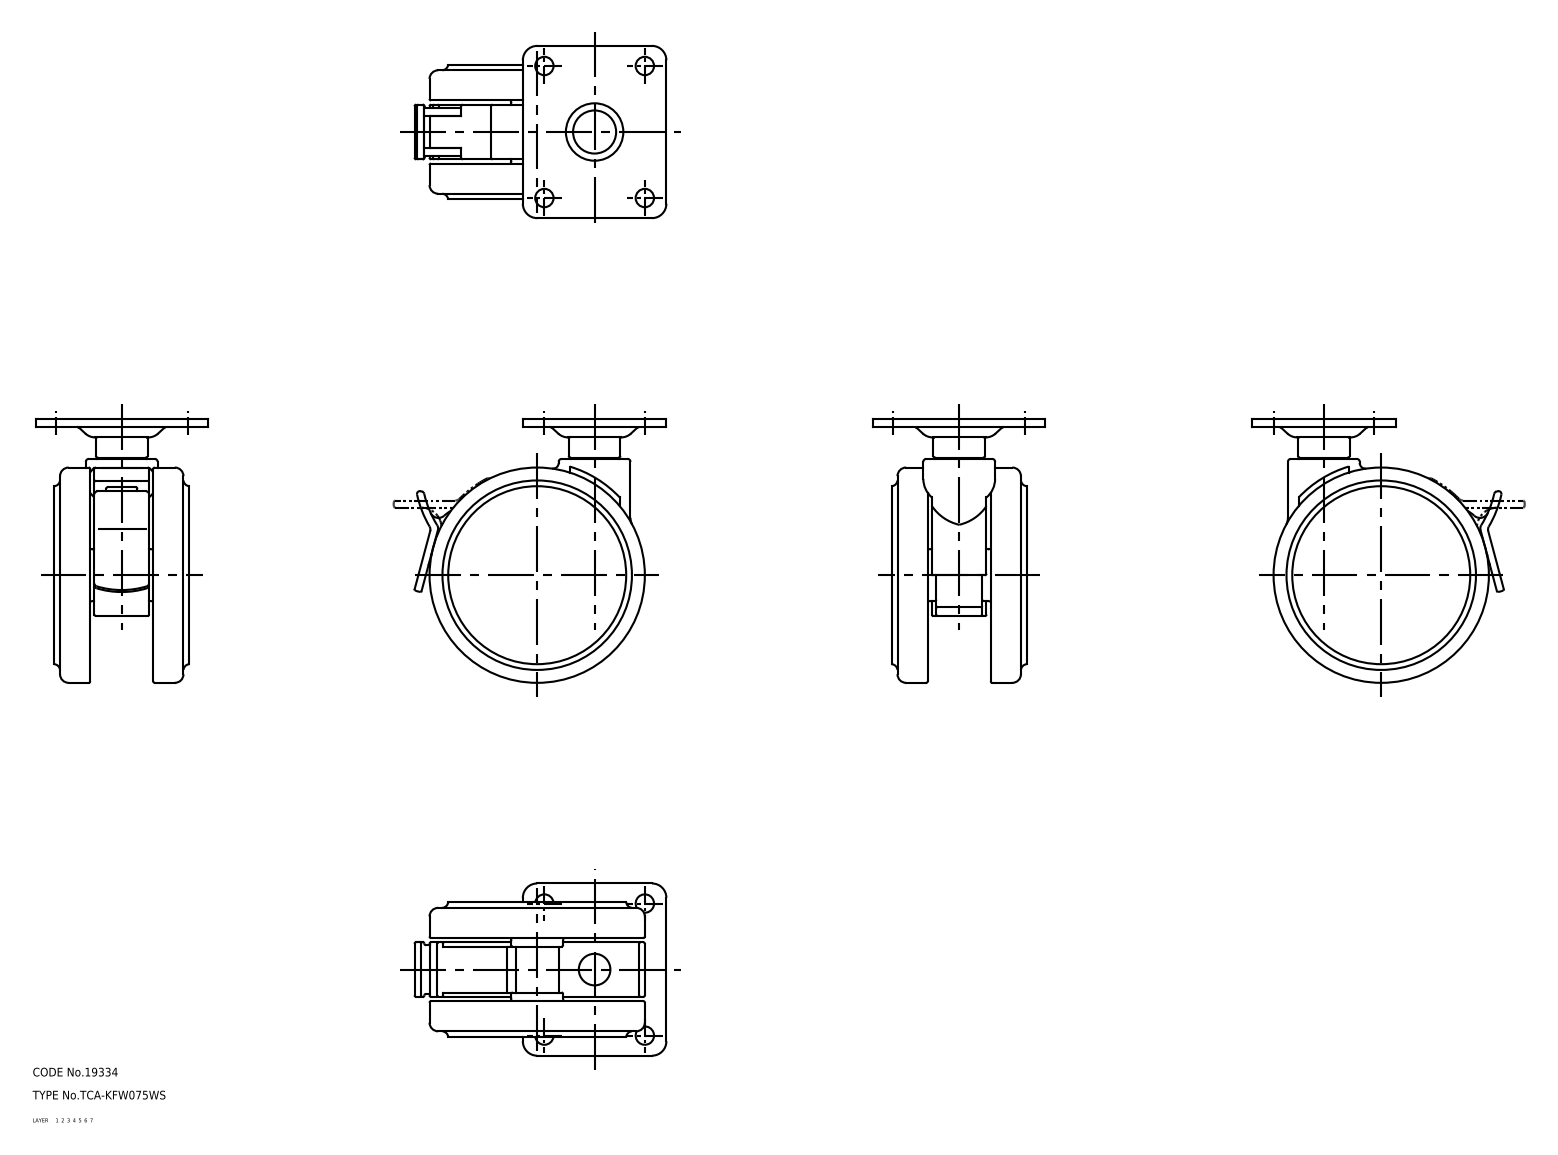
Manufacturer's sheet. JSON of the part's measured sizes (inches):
{"part_name": "main shaft; wheel_mr; wheel; lever (+2 more)", "step_written_by": "SolidWorks 2015 (AUTOMOTIVE_DESIGN)", "units": "inches", "bodies": {"solids": 6, "faces": 284, "planar": 57, "cylindrical": 118, "other": 109}, "overall_size": [3.622, 3.455, 2.362], "volume_in3": 9.999, "surface_area_in2": 71.32, "round_holes": [[0.252, 4], [0.236, 1], [1.693, 1]], "round_bosses_or_shafts": [[0.709, 2], [2.953, 1], [0.984, 1], [0.669, 1], [0.591, 1]], "partial_cylinders_radius": [[0.02, 41], [0.197, 4], [0.039, 2], [0.079, 2], [0.118, 2], [1.398, 2], [0.114, 1], [0.276, 1]], "face_to_face_distances": [0.118, 0.492, 1.358, 0.059, 0.866, 0.551, 0.748, 0.807, 1.85, 1.299], "hole_center_spacings": [1.138, 1.378, 1.811, 2.276]}
